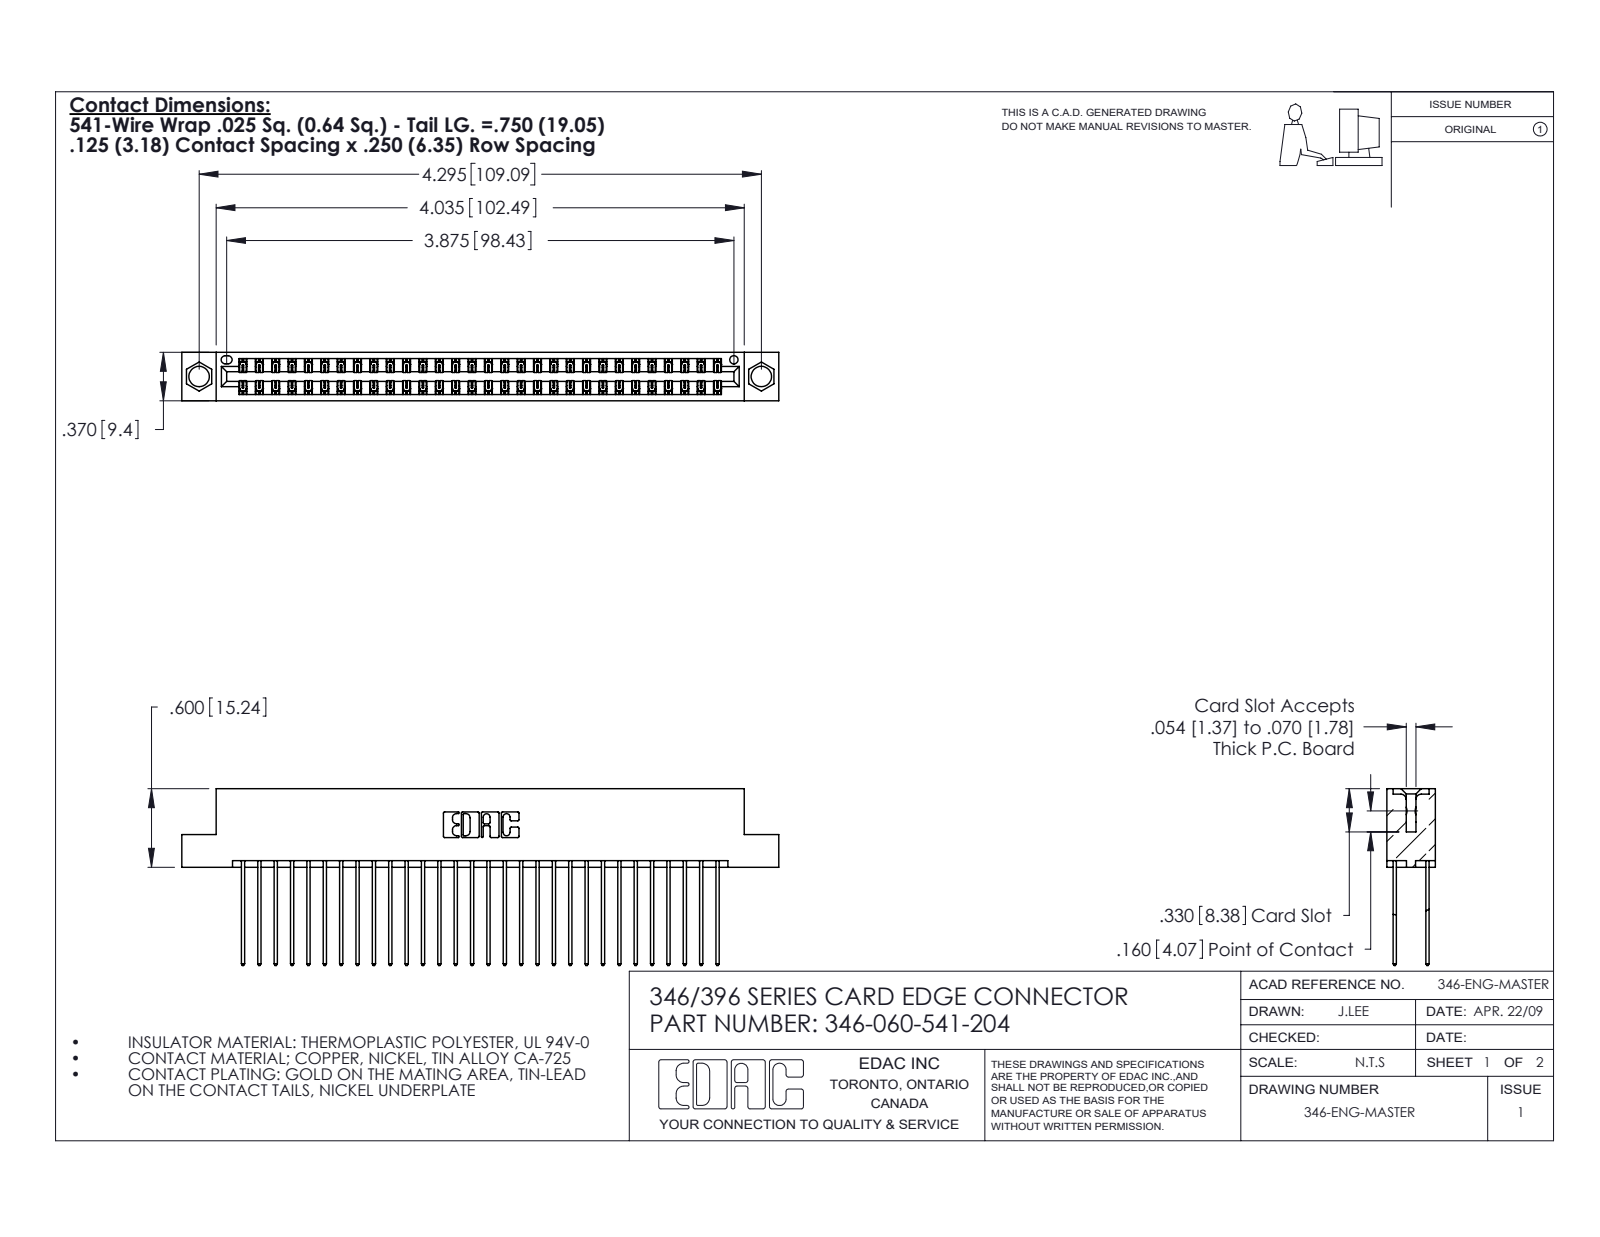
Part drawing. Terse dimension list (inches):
name: 345-292-001_345-293-141; 346-060-541-204; 346 Part_Flush Mounting Lugs - 0.156 Dia-TH
written by: SolidWorks 2020 (CONFIG_CONTROL_DESIGN)
unit: in
bodies: 61 solids, 3256 faces (2190 planar, 1066 cylindrical, 0 other)
size: 4.56 × 1.35 × 0.37
volume: 0.698 in³; area: 26.4 in²
holes: 2× ⌀0.156, 1× ⌀0.064
rounds: 90× R0.006, 60× R0.01, 22× R0.01, 6× R0.007, 6× R0.031, 3× R0.026, 2× R0.014, 2× R0.022
face distances: 0.048, 0.322, 0.25, 0.072, 0.298, 0.025, 0.37, 0.275, 0.225, 0.148
hole spacings: 0.246, 4.087, 4.295
